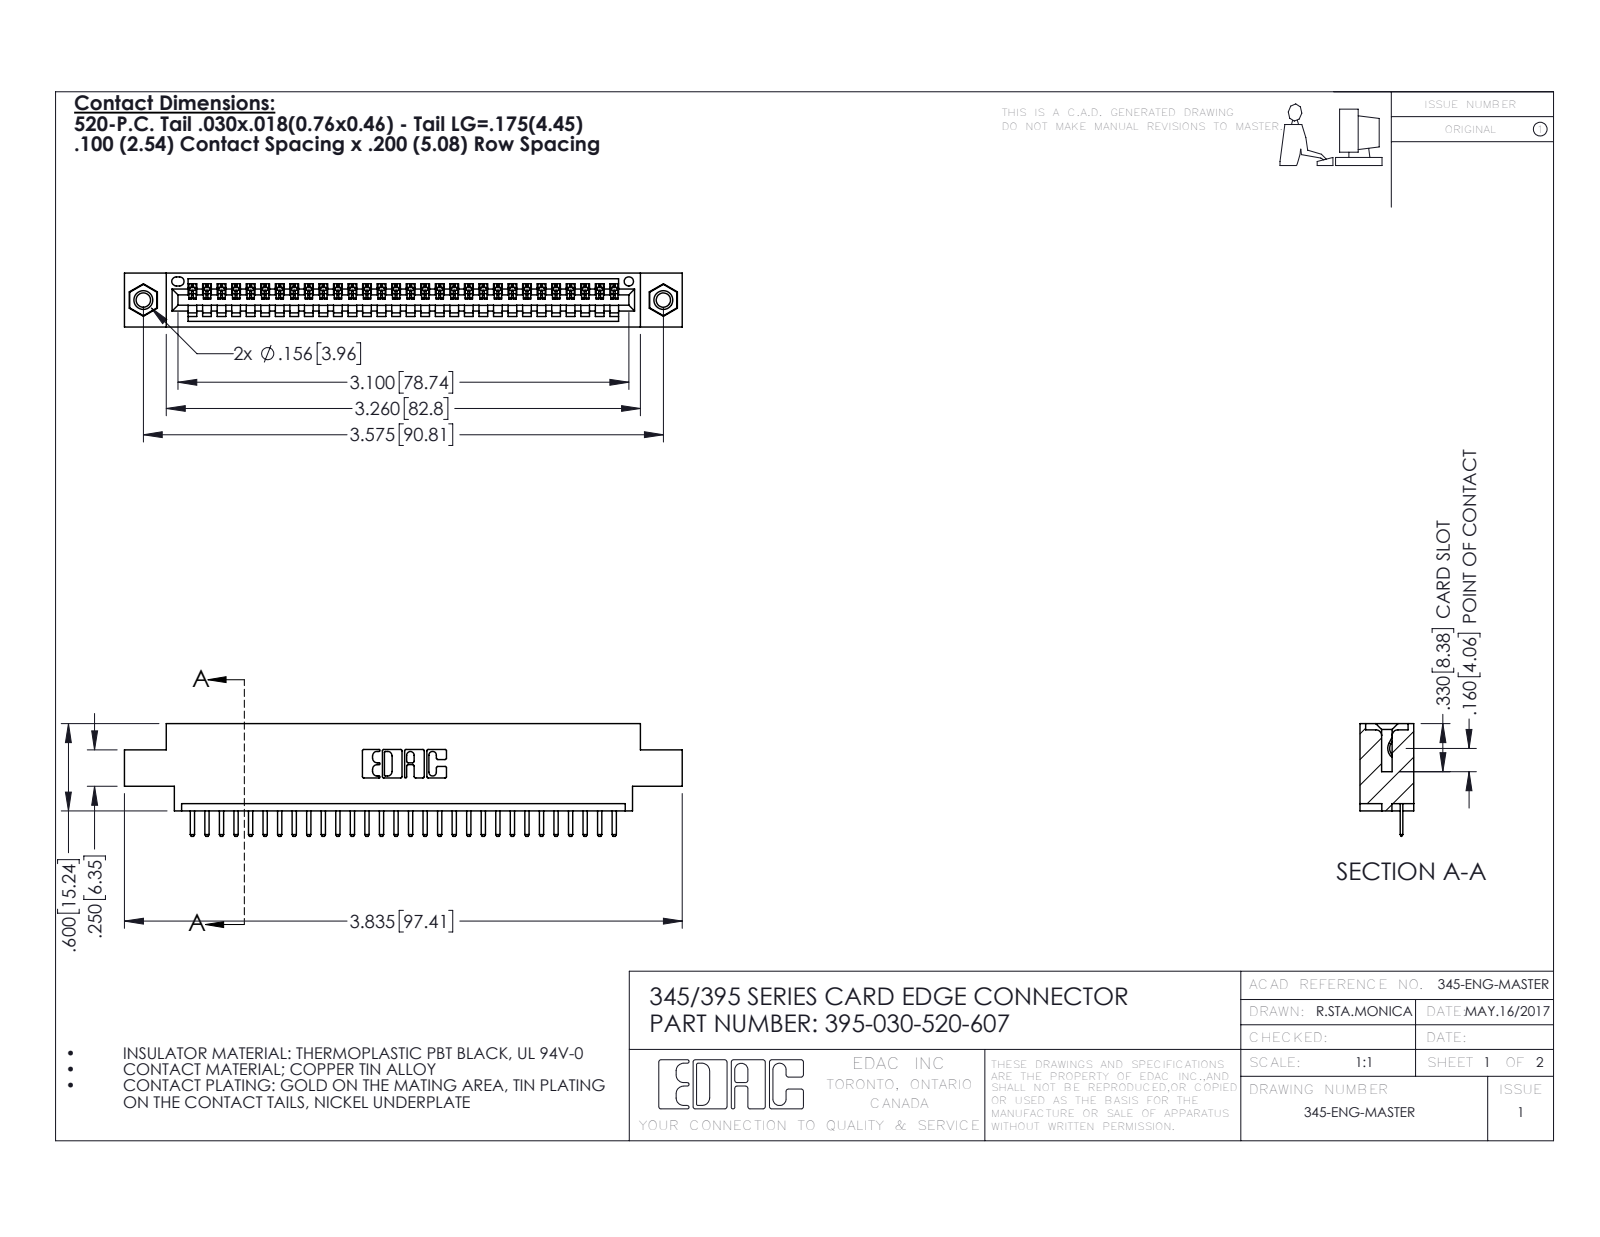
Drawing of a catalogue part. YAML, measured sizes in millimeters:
part_name: "395-030-520-607; 345-250-001_345-250-005-103; 345 Part_0.170 Offset - 0.156 Dia-TI; 345-292-001_345-293-120"
step_written_by: "SolidWorks 2016 (CONFIG_CONTROL_DESIGN)"
units: millimeters
bodies: {solids: 33, faces: 2050, planar: 1376, cylindrical: 658, other: 16}
overall_size: [97.4, 19.7, 9.4]
volume: 8950
surface_area: 11590
round_holes:
  - {diameter: 2.5, count: 2}
  - {diameter: 3.2, count: 2}
  - {diameter: 4, count: 2}
  - {diameter: 1.6, count: 1}
round_bosses_or_shafts:
  - {diameter: 3.9, count: 2}
partial_cylinders:
  - {radius: 0.3, count: 62}
  - {radius: 0.2, count: 60}
  - {radius: 0.3, count: 22}
  - {radius: 0.2, count: 6}
  - {radius: 0.8, count: 6}
  - {radius: 0.7, count: 3}
  - {radius: 0.8, count: 2}
  - {radius: 1, count: 2}
face_to_face_distances: [1.8, 7.6, 9.4, 5.1, 2.5, 6.9, 0.6, 5.7, 1.8, 4.4]
hole_center_spacings: [6.9, 84.8, 90.8]
